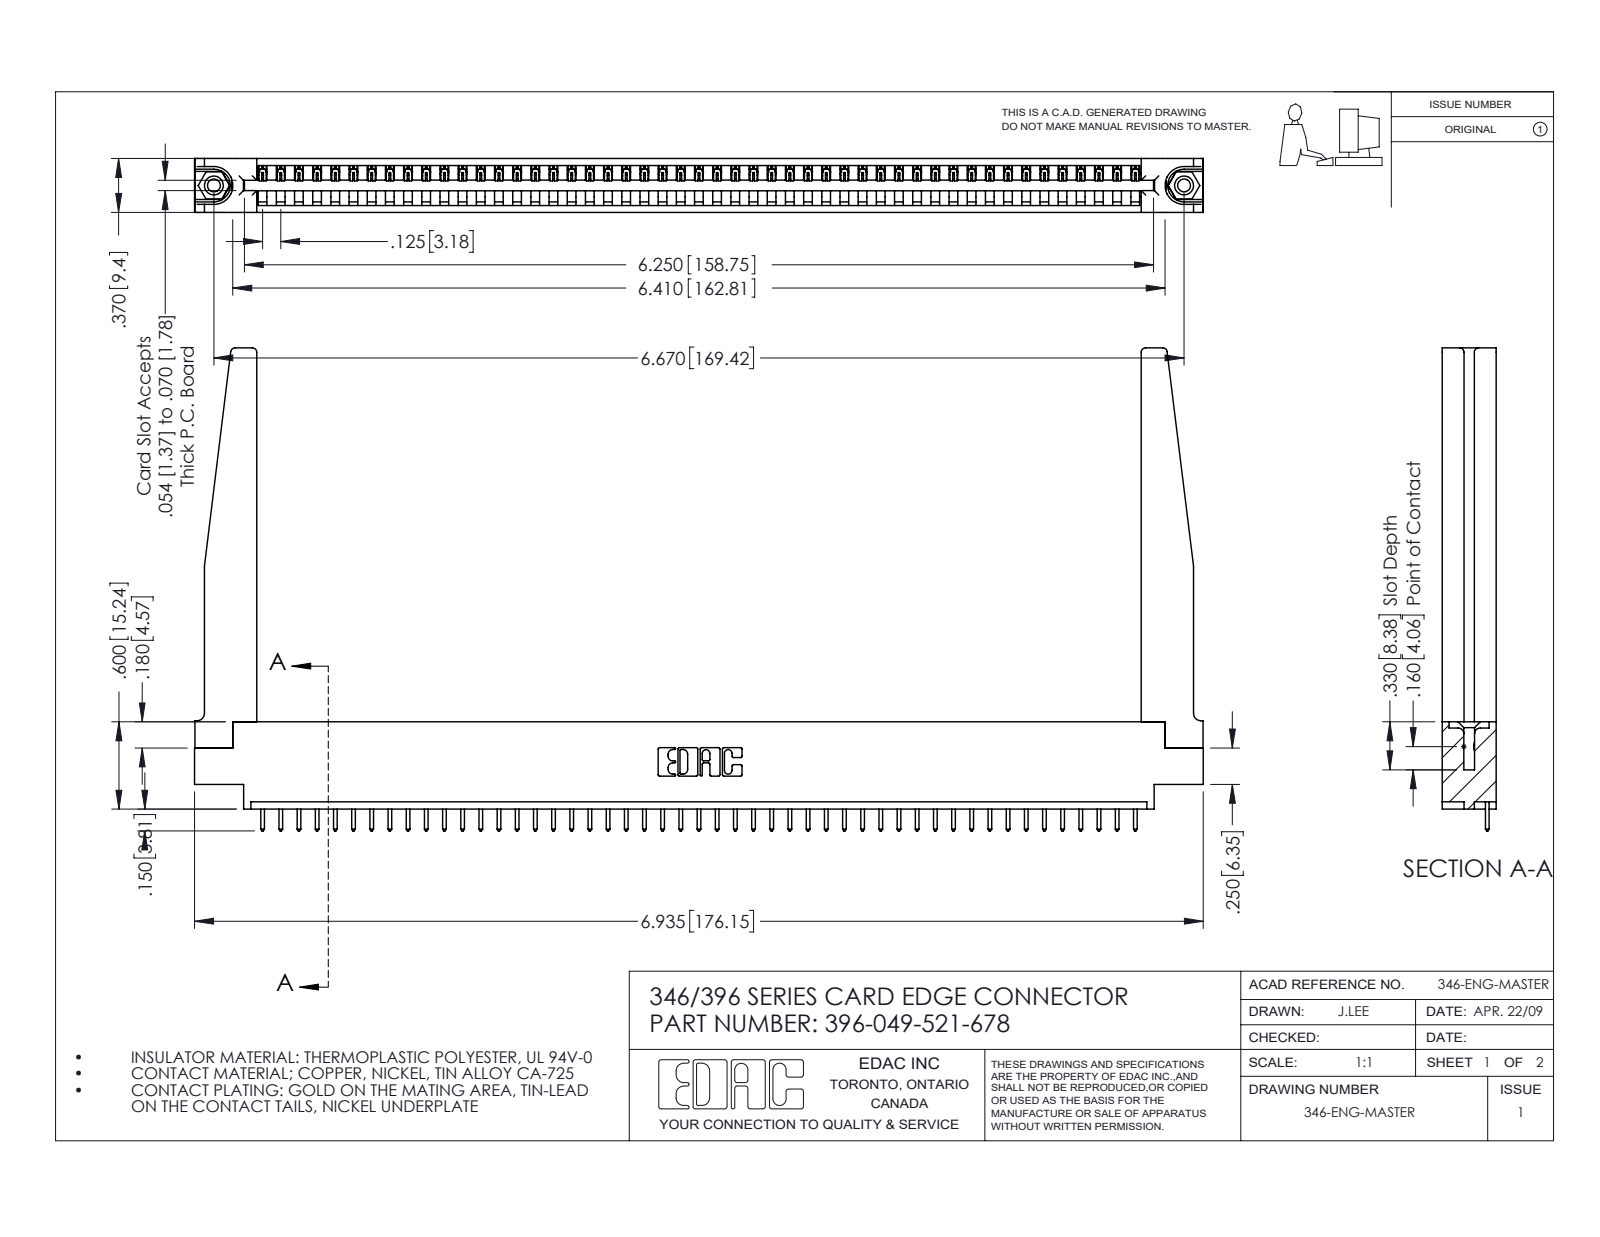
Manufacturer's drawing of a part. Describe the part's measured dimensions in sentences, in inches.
The part is named "345-292-001_345-293-121; 346 Part_0.170 Offset - 0.156 Dia-TH; 345-250-001_345-250-001-102; 396-049-521-678 (+1 more)". Its 3-D file was written by "SolidWorks 2016 (CONFIG_CONTROL_DESIGN)". It is 54 solids with 3202 faces: 2182 planar, 968 cylindrical and 52 other. Overall it measures 6.935 by 3.32 by 0.37 inches. Its volume is 1.436 cubic inches and its surface area 41.83 square inches. Round holes: 2 of diameter 0.089, 2 of diameter 0.125, 2 of diameter 0.156, 1 of diameter 0.064. Round bosses or shafts: 2 of diameter 0.155. Partial cylindrical surfaces (rounded edges, fillets, slot ends): 98 of radius 0.006, 98 of radius 0.01, 22 of radius 0.01, 8 of radius 0.03, 6 of radius 0.007, 6 of radius 0.031, 3 of radius 0.026, 2 of radius 0.031. The main face-to-face distances are 0.37, 0.048, 0.322, 0.072, 0.148, 0.15, 0.25, 0.298, 0.025, 0.222. The hole center spacings are 0.246, 6.461, 6.67.
